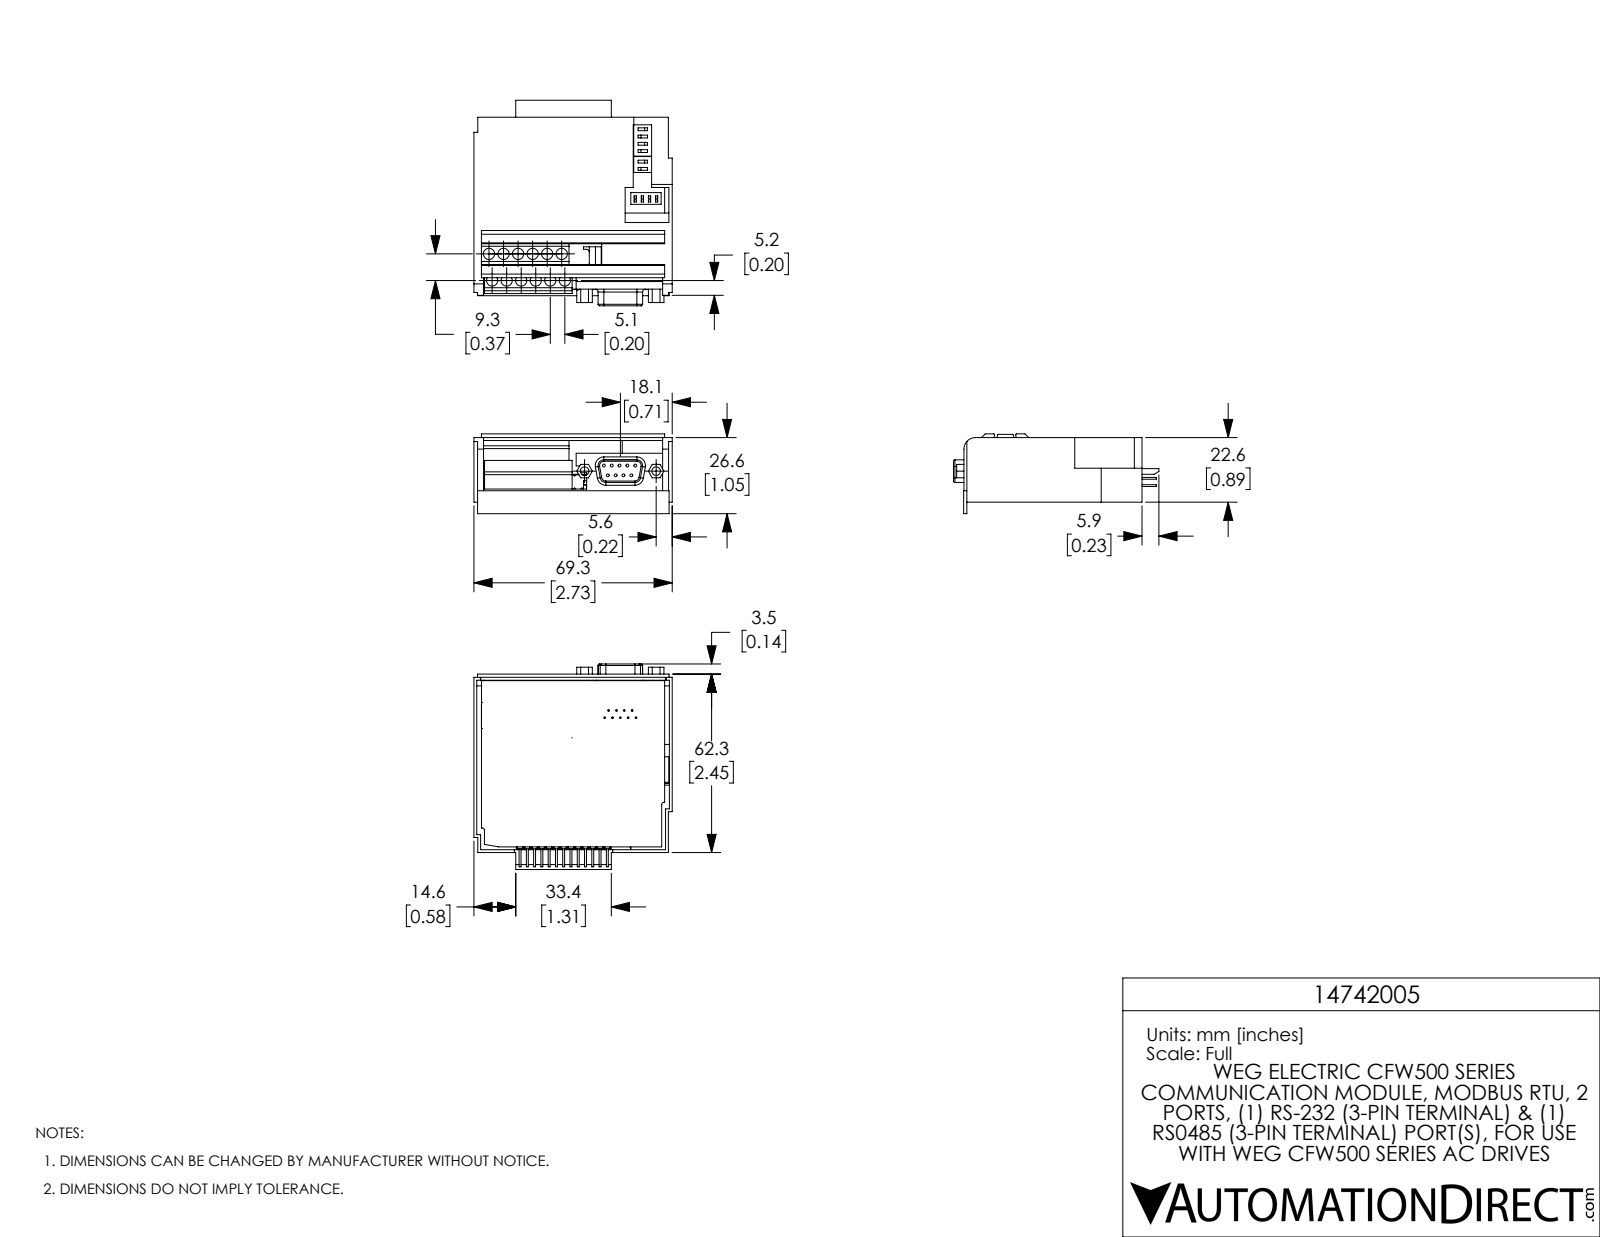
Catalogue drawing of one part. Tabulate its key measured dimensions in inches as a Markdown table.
| quantity | value |
| --- | --- |
| part name | 14742005_ MODULO COMUNICACAO CFW500_CRS232 Coord nc |
| STEP written by | SolidWorks 2017 (AUTOMOTIVE_DESIGN) |
| units | inches |
| bodies | 2 solids, 689 faces (551 planar, 112 cylindrical, 26 other) |
| overall size | 2.824 × 2.726 × 1.096 |
| volume | 1.651 in³ |
| surface area | 48.6 in² |
| round holes (diameter × count) | 0.039 × 9, 0.154 × 6, 0.155 × 6, 0.118 × 2, 0.122 × 1 |
| round bosses / shafts (diameter × count) | 0.024 × 9 |
| partial cylindrical surfaces (radius × count) | 0.039 × 10, 0.079 × 6, 0.02 × 4, 0.03 × 2, 0.061 × 1, 0.118 × 1, 0.157 × 1 |
| main face-to-face distances | 0.039, 0.063, 0.667, 0.73, 0.707, 0.77, 2.687, 2.727, 0.051, 2.413 |
| hole center spacings | 0.2, 0.144, 0.4, 0.108, 0.21, 0.369, 0.6, 0.216 |
